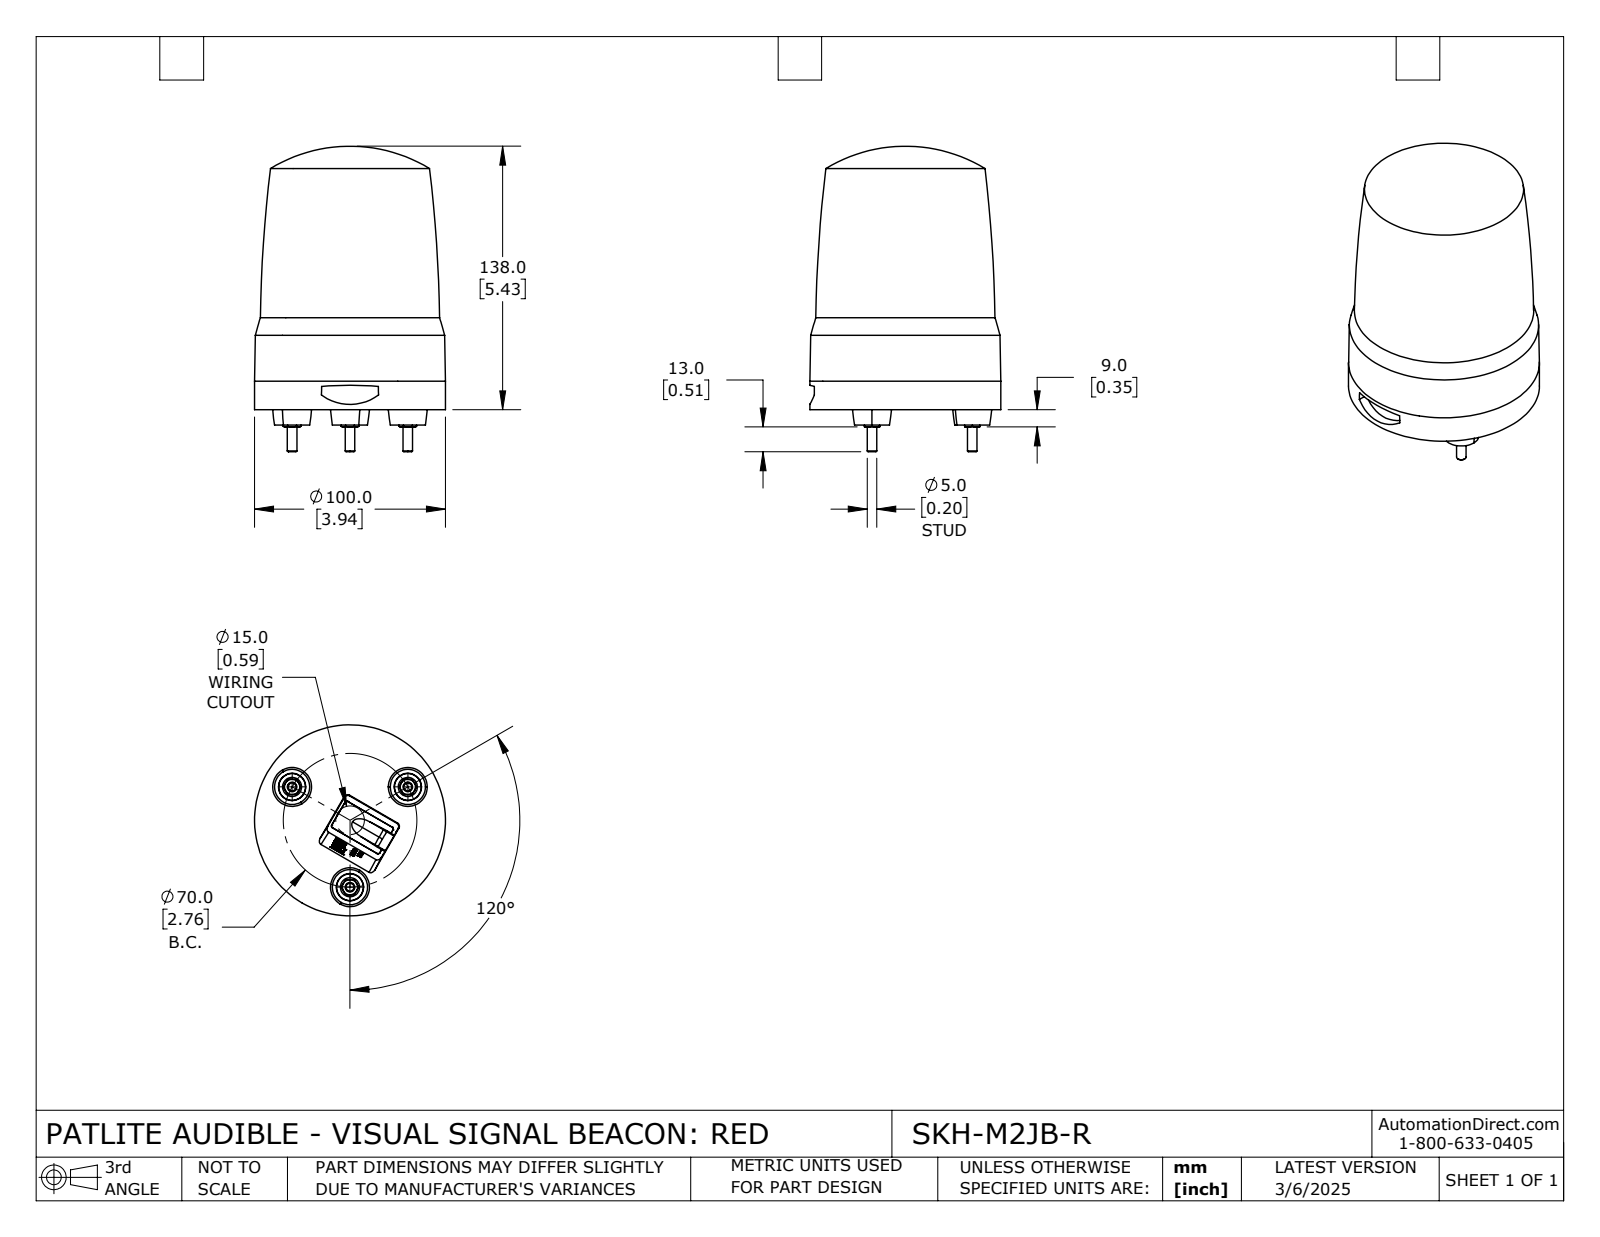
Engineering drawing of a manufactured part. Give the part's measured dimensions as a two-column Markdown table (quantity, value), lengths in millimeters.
| quantity | value |
| --- | --- |
| part name | SKH-M2JB-R |
| STEP written by | SolidWorks 2024 (CONFIG_CONTROL_DESIGN) |
| units | millimeters |
| bodies | 1 solid, 446 faces (211 planar, 22 cylindrical, 213 other) |
| overall size | 160 × 100 × 100 |
| volume | 900 363 mm³ |
| surface area | 55 433 mm² |
| round bosses / shafts (diameter × count) | 10 × 3, 5 × 3, 100 × 1 |
| partial cylindrical surfaces (radius × count) | 2 × 4, 5.05 × 2, 45 × 1, 80.12 × 1 |
| main face-to-face distances | 8, 14.85, 6.85, 1.6, 16.45, 8.45, 3.8, 4.2, 11.05, 12.65 |
